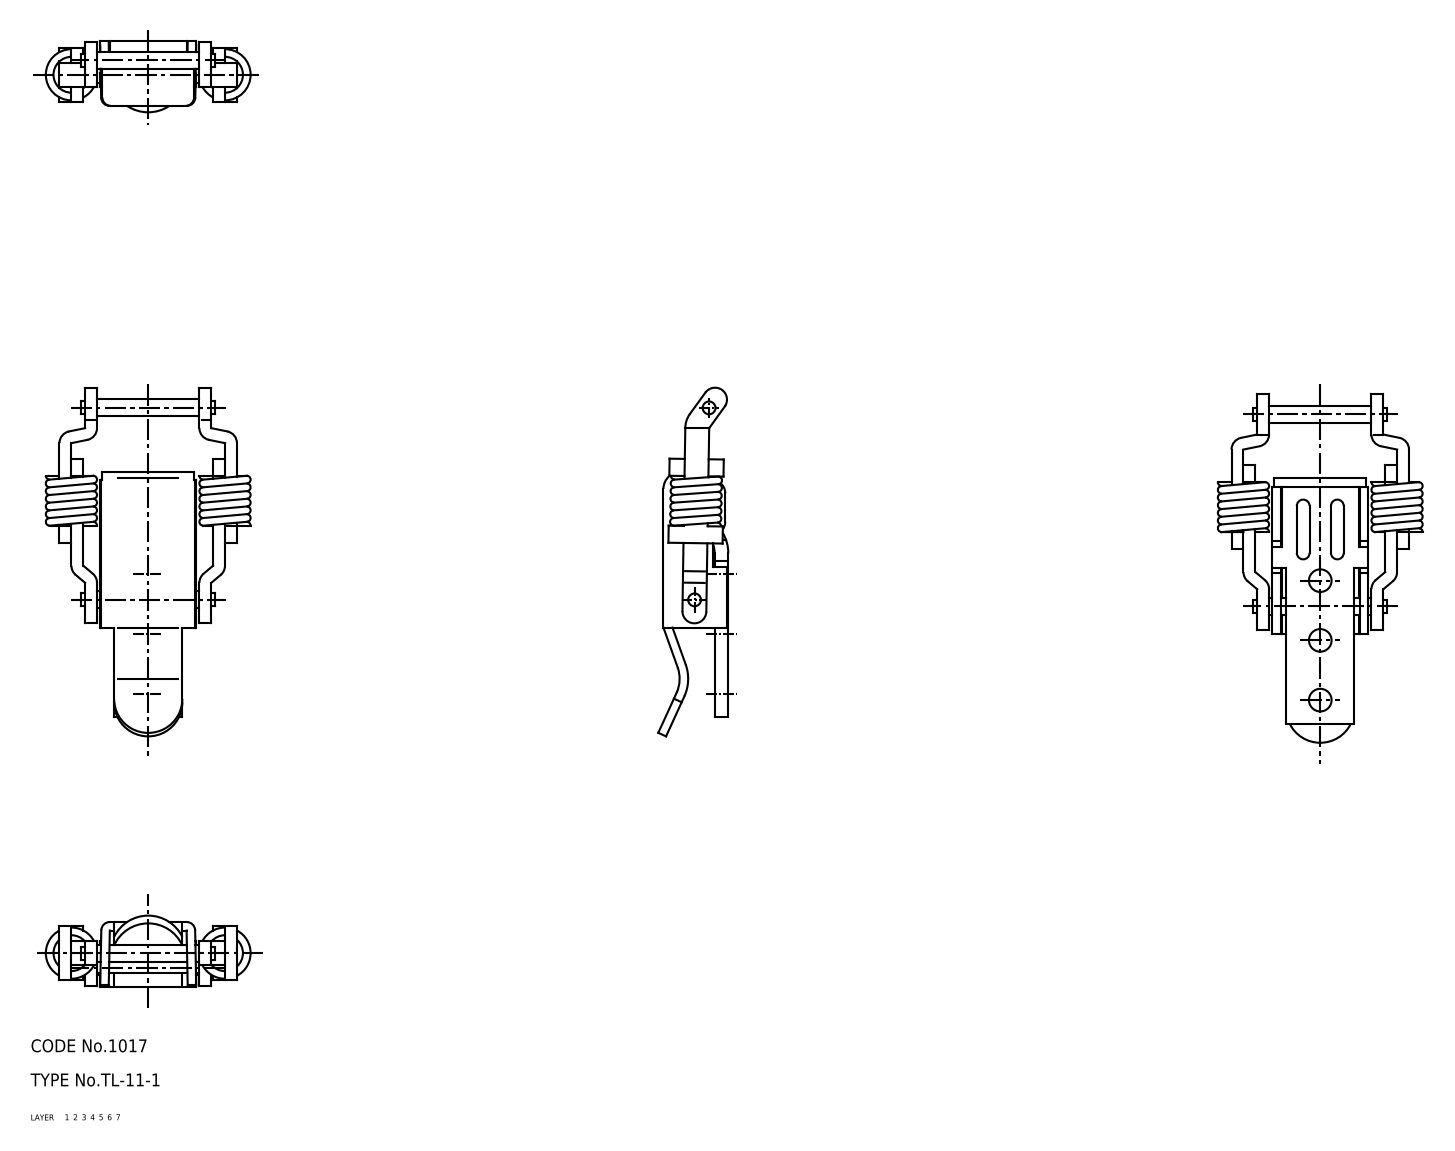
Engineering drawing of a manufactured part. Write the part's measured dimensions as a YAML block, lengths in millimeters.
part_name: "spring; shaft; arm_B_mr; lever (+5 more)"
step_written_by: "CADfix (AUTOMOTIVE_DESIGN)"
units: millimeters
bodies: {solids: 10, faces: 264, planar: 0, cylindrical: 0, other: 264}
overall_size: [80.5, 48.01, 16.4]
volume: 11766
surface_area: 13828
